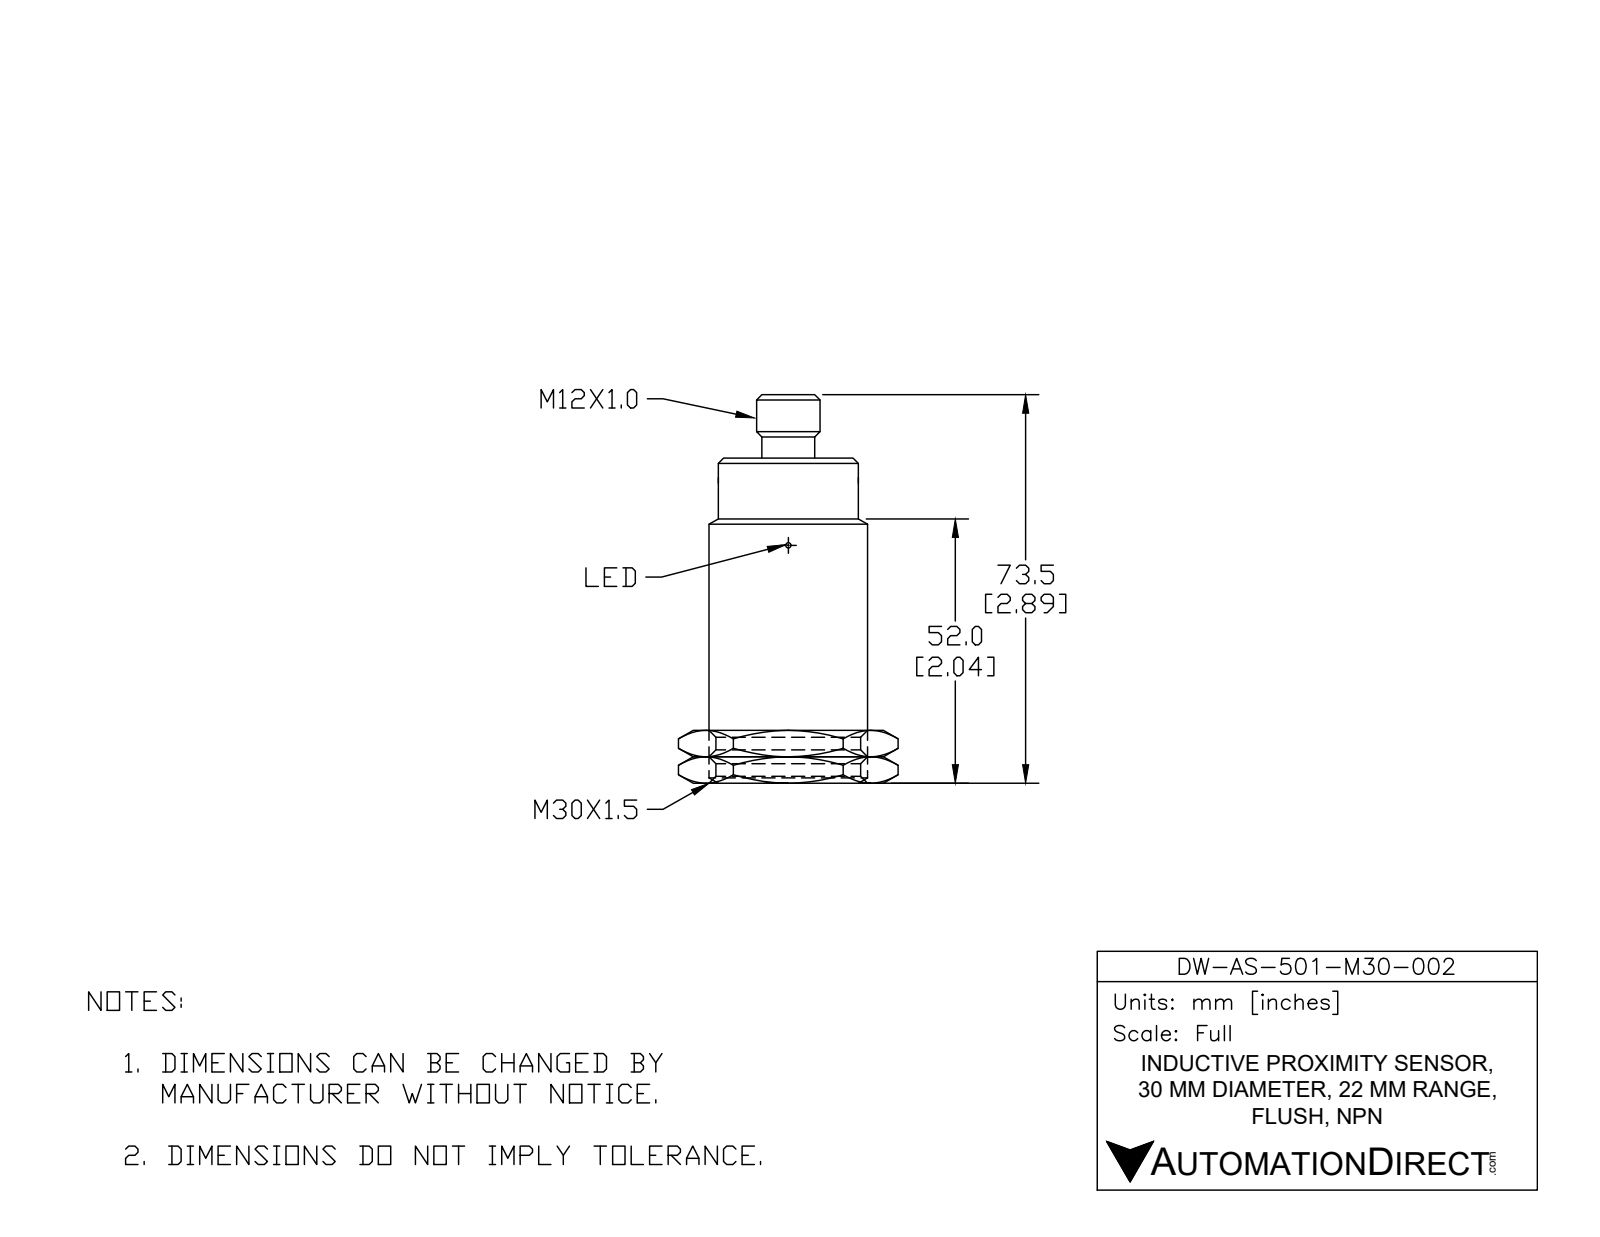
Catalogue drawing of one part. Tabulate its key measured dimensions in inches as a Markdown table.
| quantity | value |
| --- | --- |
| part name | DW-AS-511-M30-002 |
| STEP written by | SolidWorks 2017 (AUTOMOTIVE_DESIGN) |
| units | inches |
| bodies | 1 solid, 38 faces (8 planar, 20 cylindrical, 10 other) |
| overall size | 2.895 × 1.181 × 1.181 |
| volume | 2.6 in³ |
| surface area | 12.11 in² |
| round holes (diameter × count) | 0.118 × 2, 0.335 × 1 |
| round bosses / shafts (diameter × count) | 0.039 × 4, 1.181 × 1, 1.083 × 1, 0.472 × 1, 0.415 × 1 |
| partial cylindrical surfaces (radius × count) | 0.022 × 2, 0.193 × 1 |
| main face-to-face distances | 2.38, 2.552, 0.172, 2.05, 0.33, 0.502, 2.895, 0.845, 0.515, 0.343 |
